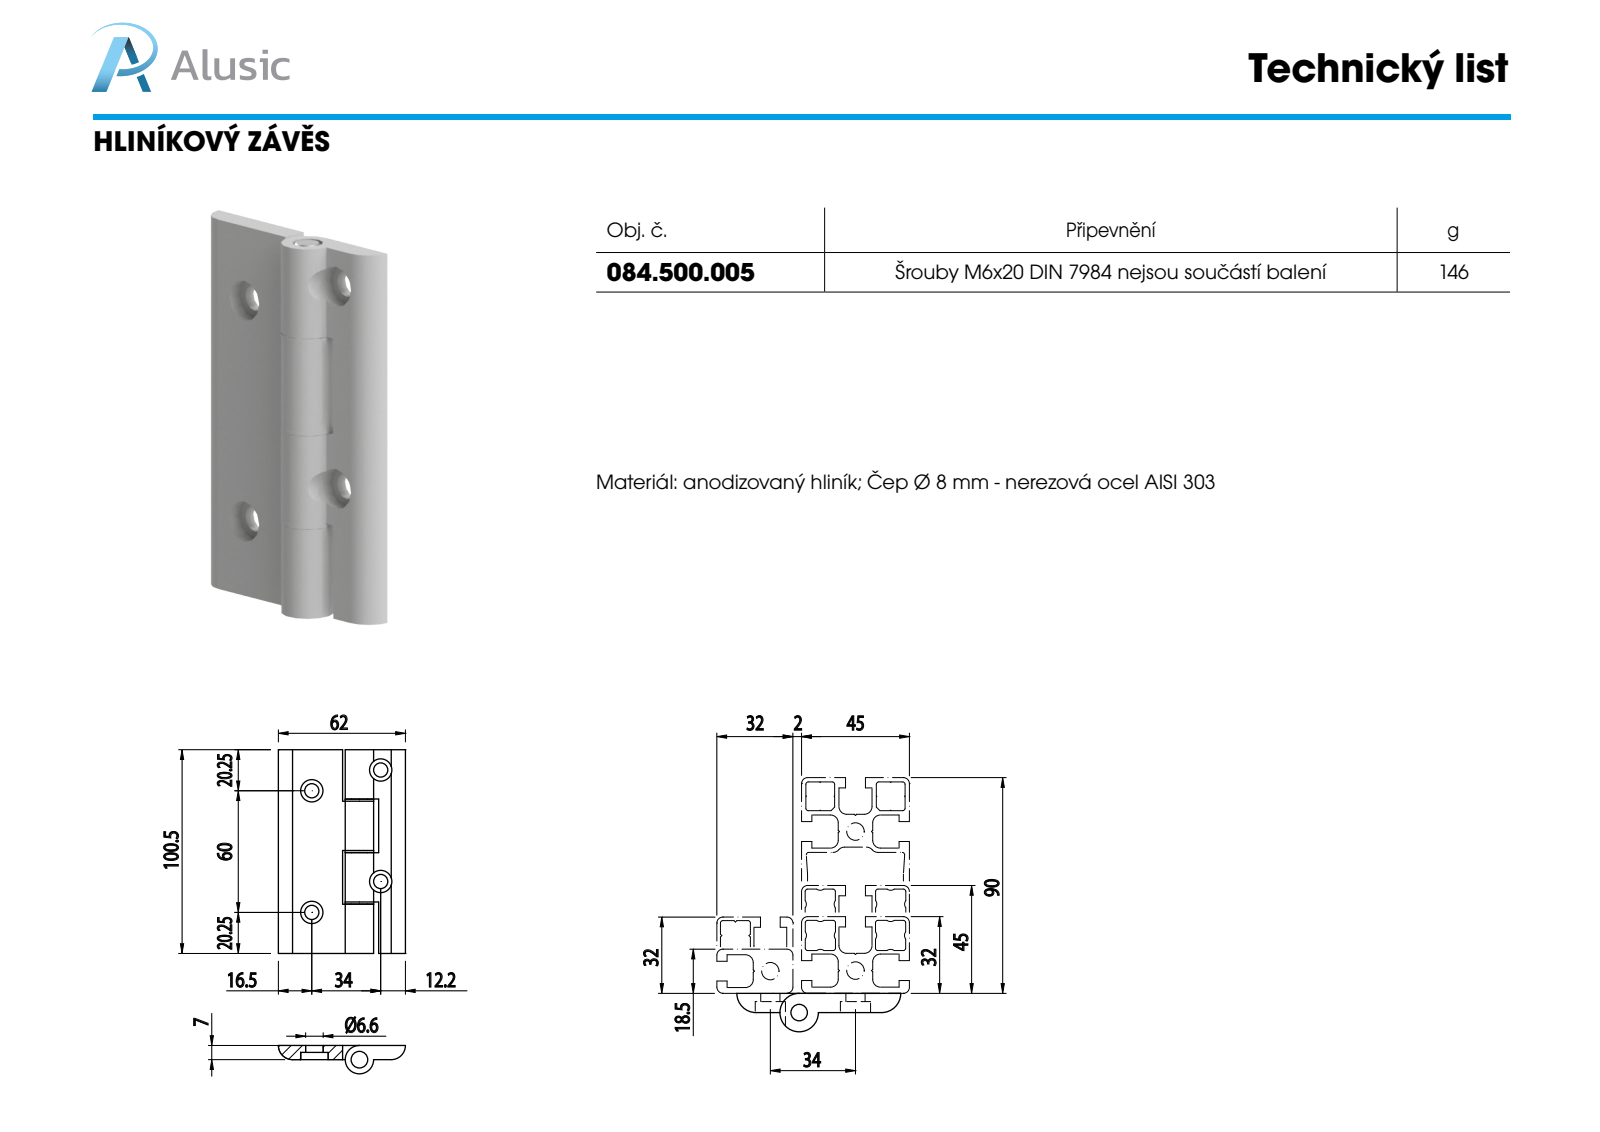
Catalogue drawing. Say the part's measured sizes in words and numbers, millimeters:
The part is named "SEMI CERNIERA_084.500.004.A; PERNO CERNIERA_084.500.004.B; 084.500.001.C; SEMI CERNIERA_084.500.005.A (+1 more)". Its 3-D file was written by "SolidWorks 2011 (CONFIG_CONTROL_DESIGN)". It is 6 solids with 202 faces: 152 planar, 46 cylindrical and 4 other. Overall it measures 100 by 47.55 by 14.1 millimeters. Its volume is 43 733 cubic millimeters and its surface area 22 770 square millimeters. Round holes: 4 of diameter 6.6, 4 of diameter 11, 1 of diameter 8.1, 1 of diameter 8.2. Round bosses or shafts: 1 of diameter 14.1, 1 of diameter 14, 1 of diameter 8. Partial cylindrical surfaces (rounded edges, fillets, slot ends): 2 of radius 6.7. The main face-to-face distances are 6.7, 7.3, 14, 0.6, 1, 25.5, 25, 24.25, 75.75, 25.25. The hole center spacings are 16.4, 19.85, 46.84, 55, 60, 71.2.
